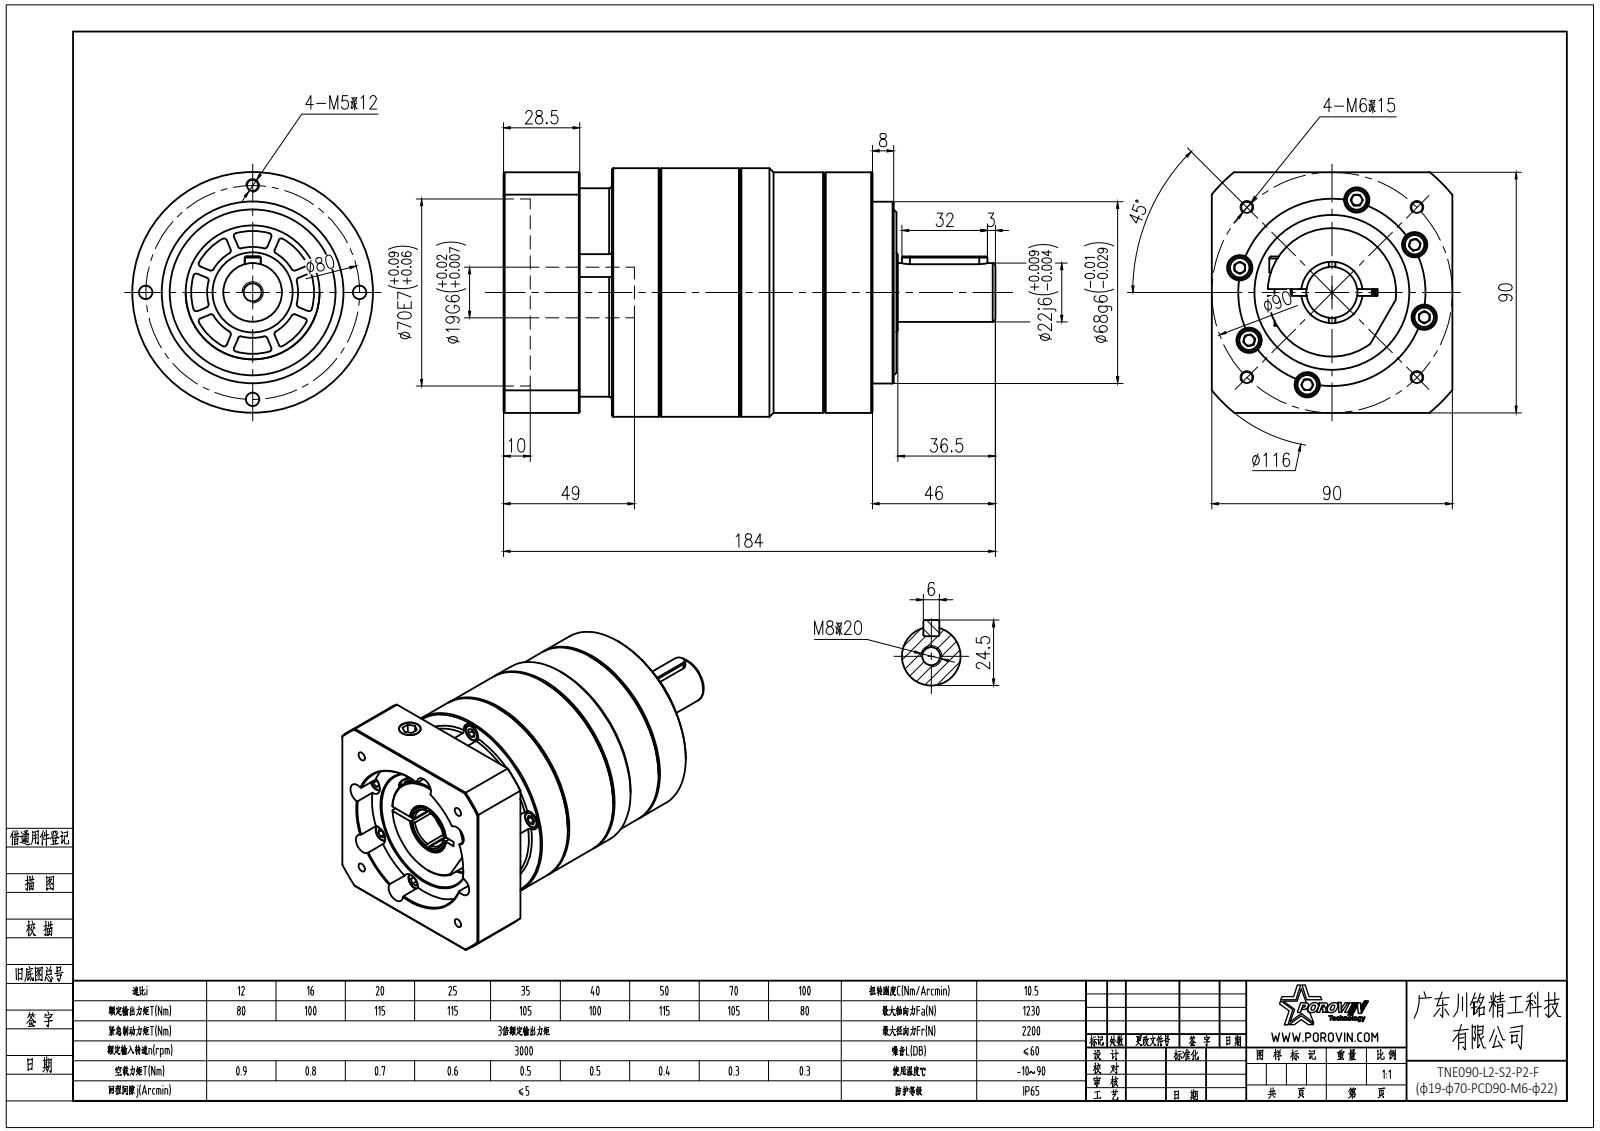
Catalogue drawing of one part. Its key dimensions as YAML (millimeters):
part_name: "hex socket set screws with flat point gb_GB_FASTENER_SCREWS_HSFP M12X12-N; hexagon socket head cap screws gb_GB_FASTENER_SCREWS_HSHCS M6X20-N; spring lock washers--normal type gb_GB_FASTENER_WASHER_SW 5; hexagon socket head cap screws gb_GB_FASTENER_SCREWS_HSHCS M5X20-N (+2 more)"
step_written_by: "SolidWorks 2016 (CONFIG_CONTROL_DESIGN)"
units: millimeters
bodies: {solids: 30, faces: 856, planar: 337, cylindrical: 319, other: 200}
overall_size: [184, 93, 93]
volume: 796984
surface_area: 152067
round_holes:
  - {diameter: 5.4, count: 10}
  - {diameter: 5.5, count: 10}
  - {diameter: 9.5, count: 10}
  - {diameter: 5, count: 9}
  - {diameter: 4.2, count: 6}
  - {diameter: 6.5, count: 1}
  - {diameter: 6.8, count: 1}
  - {diameter: 8.5, count: 1}
  - {diameter: 10.2, count: 1}
  - {diameter: 19, count: 1}
  - {diameter: 19.2, count: 1}
  - {diameter: 50, count: 1}
round_bosses_or_shafts:
  - {diameter: 8.5, count: 10}
  - {diameter: 8, count: 10}
  - {diameter: 5, count: 10}
  - {diameter: 93, count: 1}
  - {diameter: 90, count: 1}
  - {diameter: 78.5, count: 1}
  - {diameter: 78, count: 1}
  - {diameter: 68, count: 1}
partial_cylinders:
  - {radius: 1, count: 32}
  - {radius: 3, count: 2}
  - {radius: 5.5, count: 1}
  - {radius: 23, count: 1}
  - {radius: 35, count: 1}
  - {radius: 58, count: 1}
face_to_face_distances: [30, 31.5, 61.5, 88.5, 58.5, 32.5, 28.5, 90, 2.5, 94]
hole_center_spacings: [32.85, 78.55, 35.75, 75.85, 10.75, 22.73, 33.05, 40]
